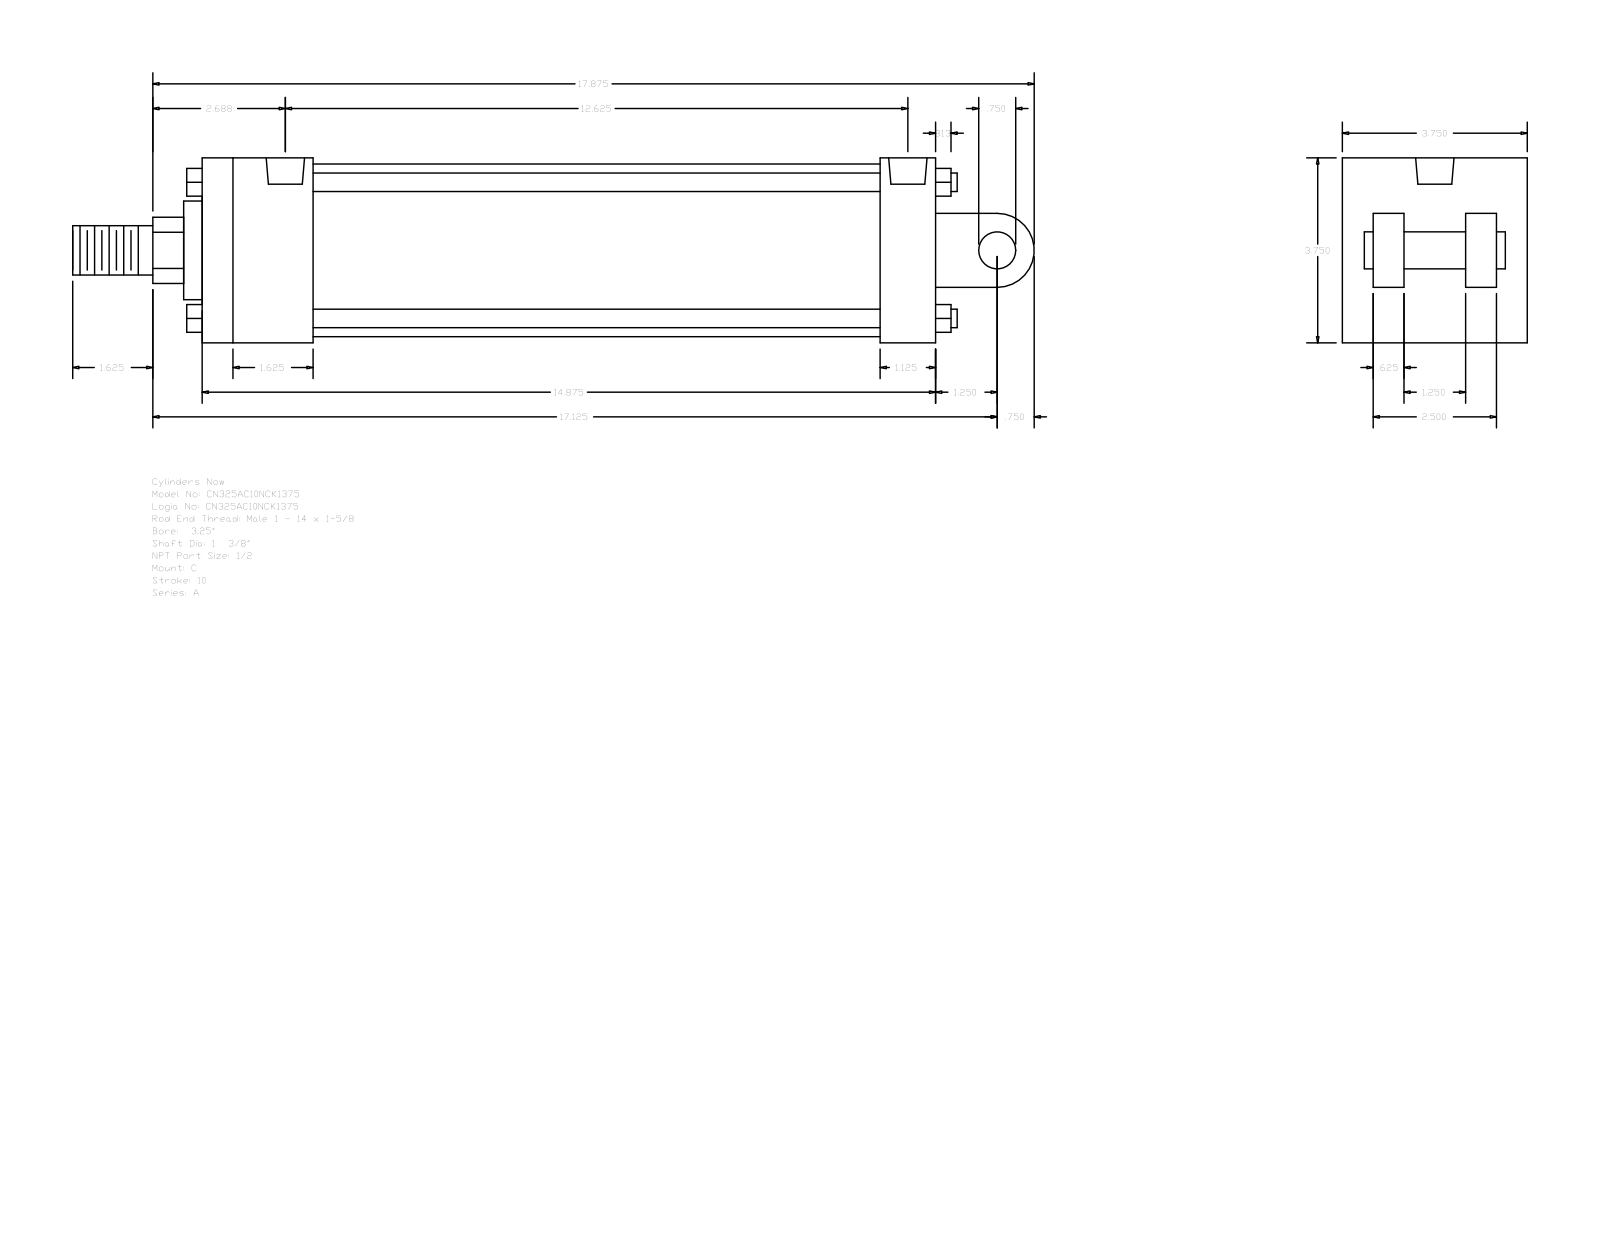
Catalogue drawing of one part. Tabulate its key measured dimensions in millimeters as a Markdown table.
| quantity | value |
| --- | --- |
| part name | A_C__0325_1.375 |
| STEP written by | GSSL Pune (CONFIG_CONTROL_DESIGN) |
| units | millimeters |
| bodies | 0 solids, 135 faces (102 planar, 33 cylindrical, 0 other) |
| overall size | 495.3 × 95.25 × 95.25 |
| round holes (diameter × count) | 8.73 × 4, 19.77 × 2 |
| round bosses / shafts (diameter × count) | 9.53 × 4, 88.9 × 1, 50.8 × 1, 34.92 × 1, 25.4 × 1, 19.05 × 1 |
| partial cylindrical surfaces (radius × count) | 17.06 × 1, 19.05 × 1 |
| main face-to-face distances | 95.24, 377.83, 15.87, 63.5, 66.67, 57.15, 28.58, 79.37, 31.74, 47.63 |
| hole center spacings | 3.18, 314.32, 317.5, 320.68 |
